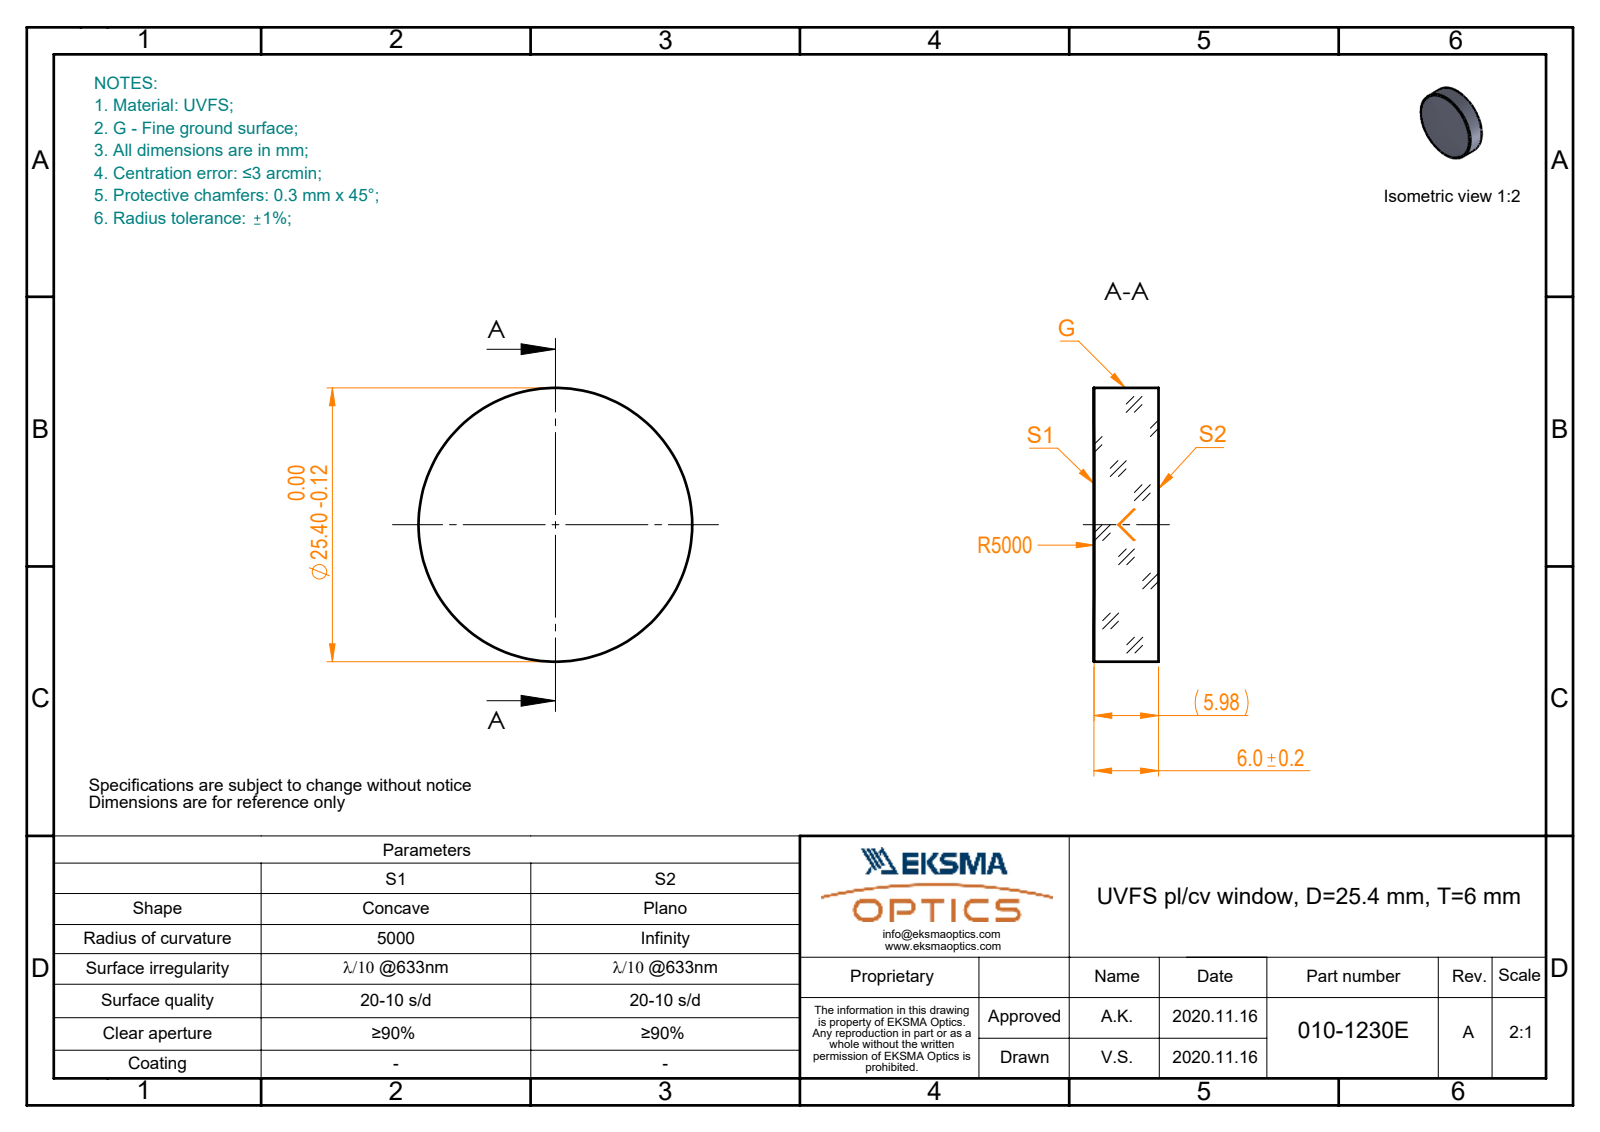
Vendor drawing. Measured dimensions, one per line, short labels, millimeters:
name: 010-1230E_UVFS_PCV_window
written by: SolidWorks 2019 (CONFIG_CONTROL_DESIGN)
unit: mm
bodies: 1 solid, 5 faces (1 planar, 2 cylindrical, 2 other)
size: 25.4 × 25.4 × 6
volume: 3 036 mm³; area: 1 492 mm²
bosses: 1× ⌀25.4
